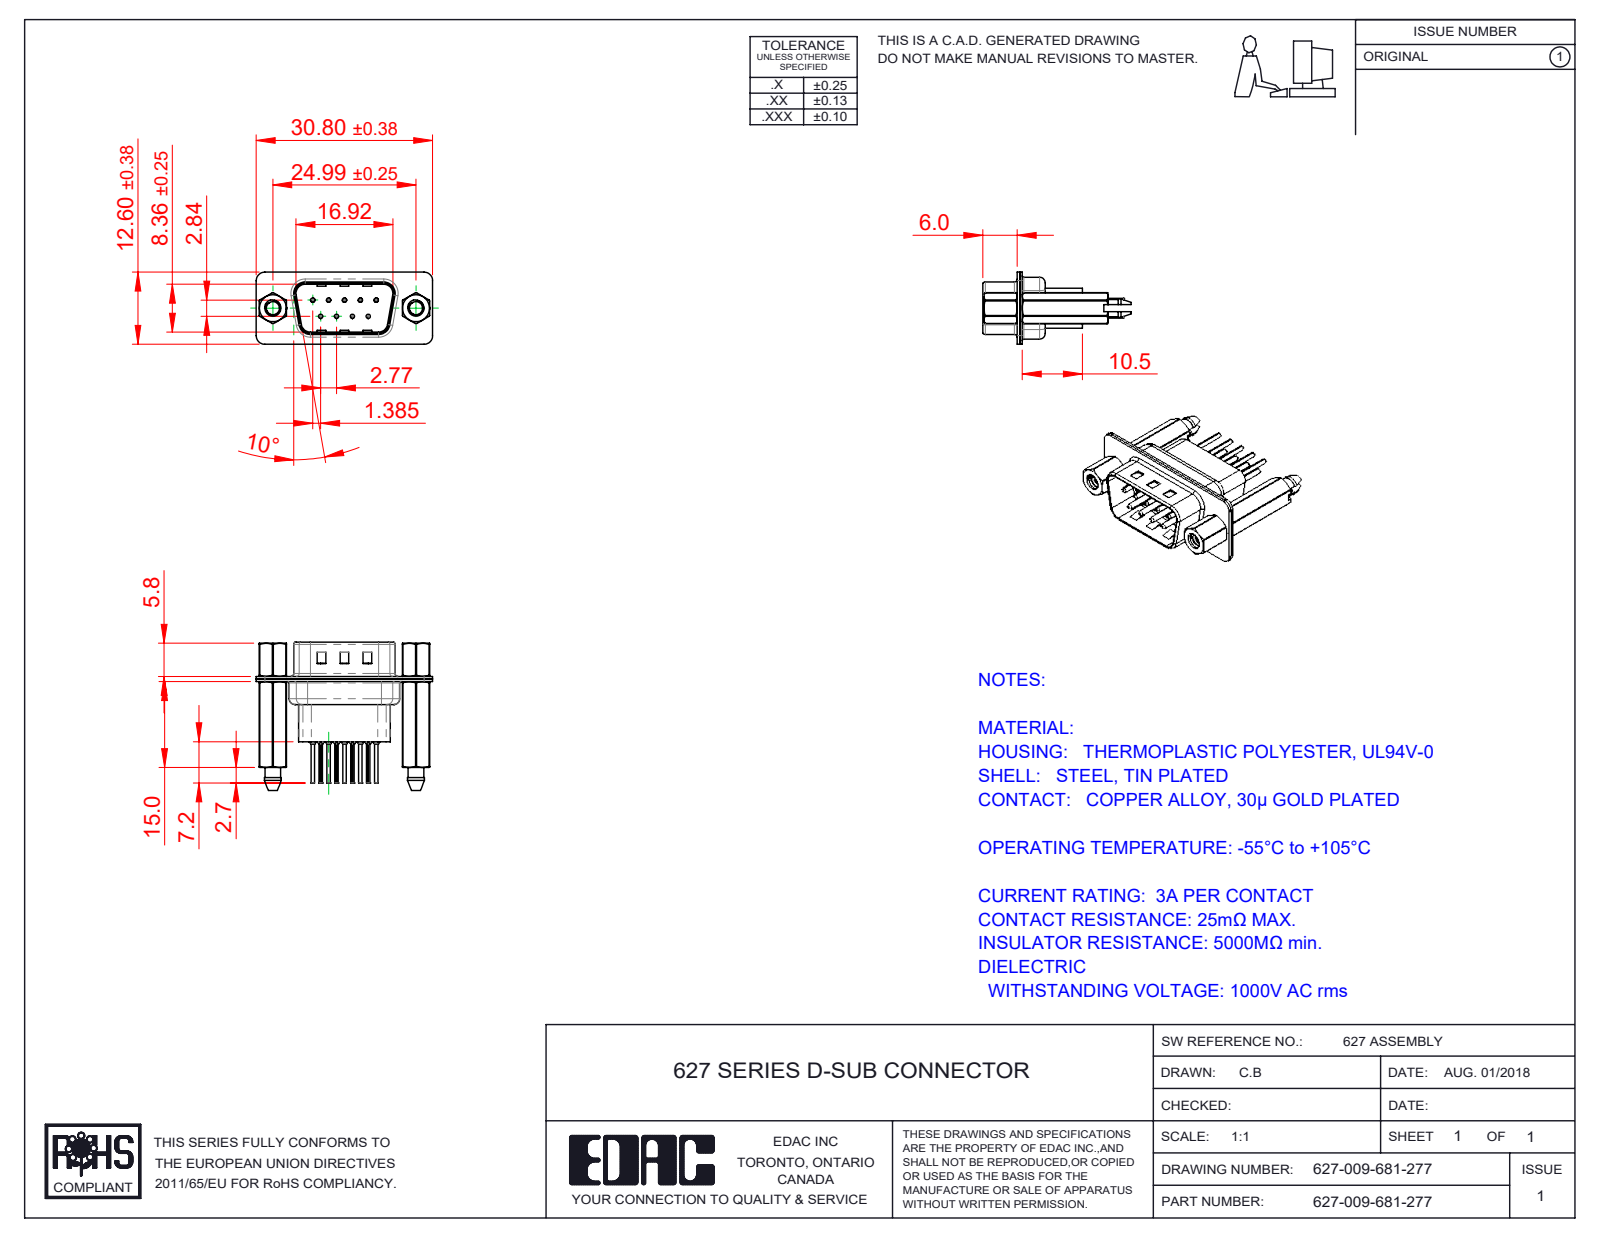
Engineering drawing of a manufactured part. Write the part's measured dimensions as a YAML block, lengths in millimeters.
part_name: "627 Housing_09 HP; 627 Shell Rear_09 Contacts; 627-009-681-277; 627 Contact Row 1_61 (+4 more)"
step_written_by: "SolidWorks 2020 (CONFIG_CONTROL_DESIGN)"
units: millimeters
bodies: {solids: 16, faces: 1420, planar: 377, cylindrical: 600, other: 443}
overall_size: [30.8, 25.9, 12.6]
volume: 2375
surface_area: 6060
round_holes:
  - {diameter: 0.2, count: 9}
  - {diameter: 0.35, count: 9}
  - {diameter: 1.1, count: 9}
  - {diameter: 1.6, count: 9}
  - {diameter: 2.26, count: 2}
  - {diameter: 2.29, count: 2}
  - {diameter: 4, count: 2}
  - {diameter: 4.8, count: 2}
round_bosses_or_shafts:
  - {diameter: 2, count: 9}
  - {diameter: 1.5, count: 9}
  - {diameter: 0.75, count: 9}
  - {diameter: 0.6, count: 9}
  - {diameter: 4.9, count: 2}
  - {diameter: 2.79, count: 2}
partial_cylinders:
  - {radius: 1.5, count: 20}
  - {radius: 0.1, count: 18}
  - {radius: 2, count: 12}
  - {radius: 1.6, count: 10}
  - {radius: 0.5, count: 8}
  - {radius: 0.25, count: 4}
  - {radius: 0.6, count: 4}
  - {radius: 0.65, count: 4}
face_to_face_distances: [0.45, 0.4, 0.9, 4.76, 0.82, 9.58, 1.4, 1.5, 0.68, 7.68]
hole_center_spacings: [3.16, 2.77, 5.54, 5.03, 5.04, 8.31, 7.48, 7.49]
